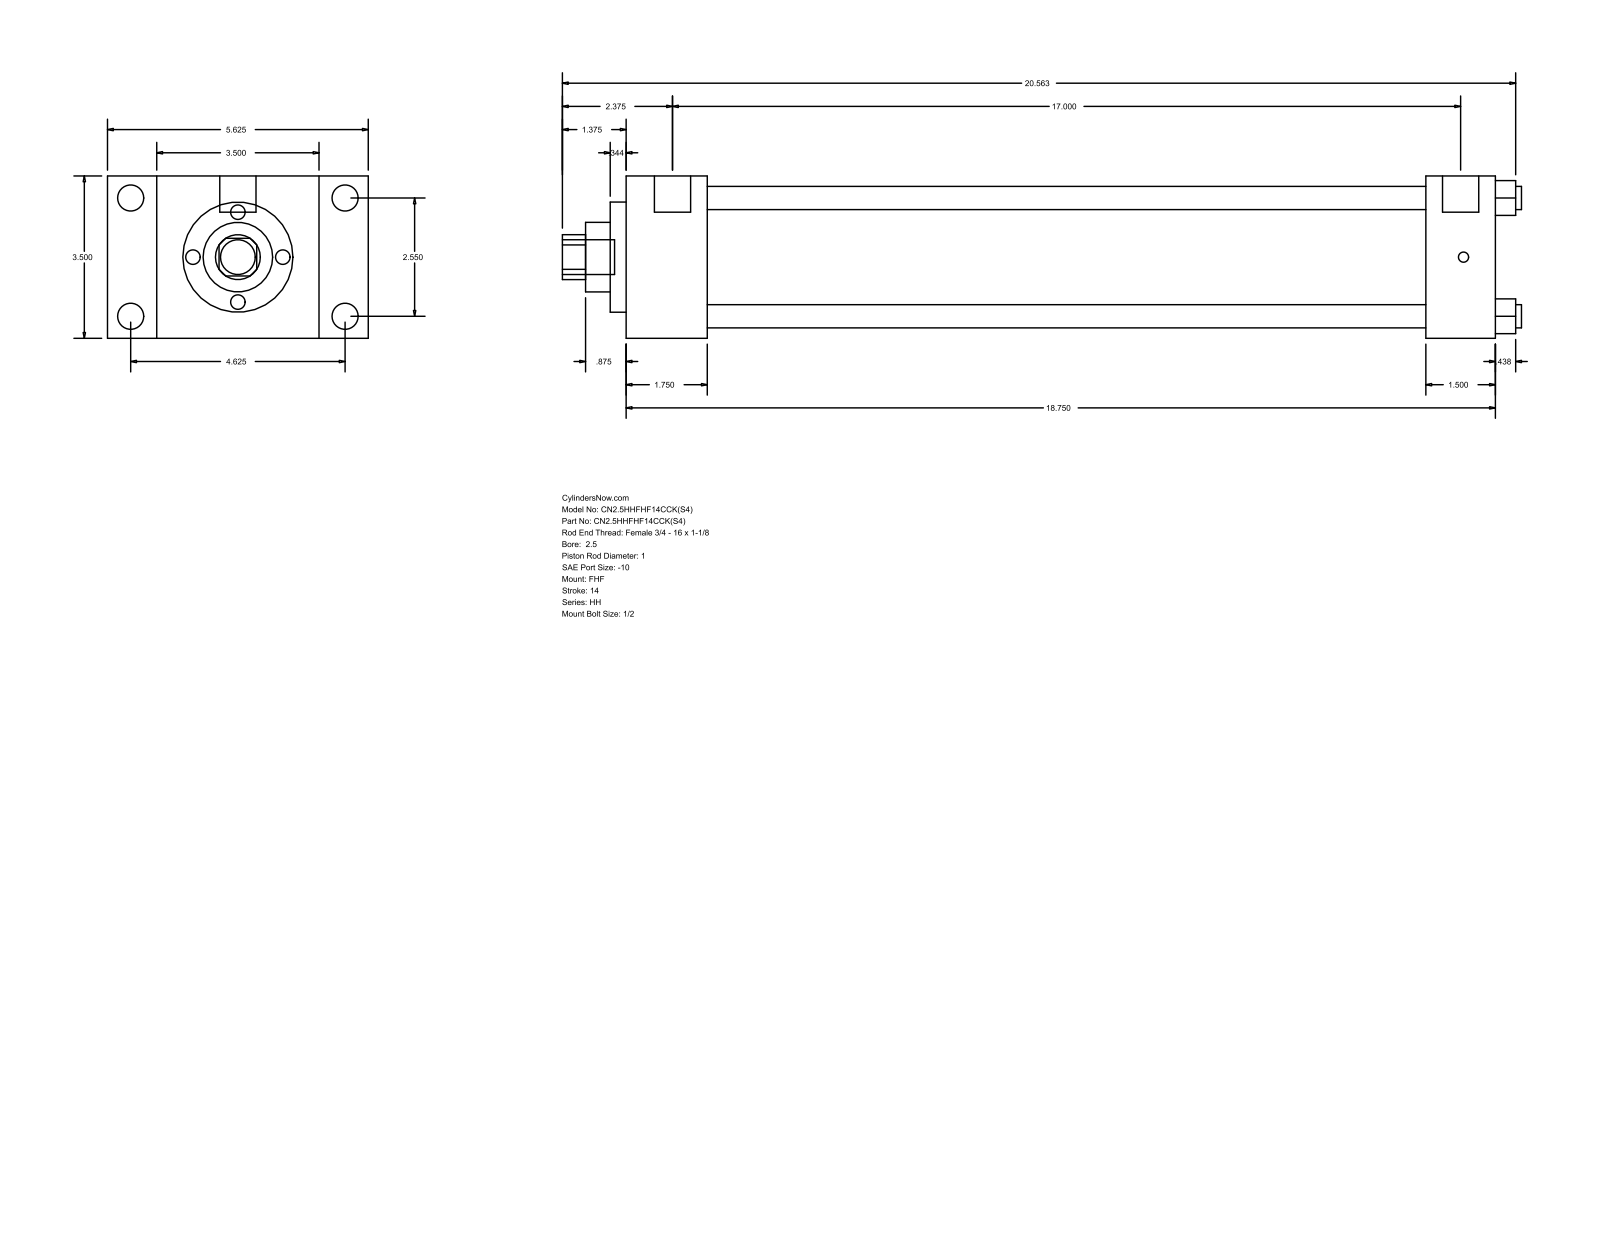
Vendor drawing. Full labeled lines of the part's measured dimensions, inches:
Part name (STEP PRODUCT): HH_FHF__0250_1
STEP written by: GSSL Pune (CONFIG_CONTROL_DESIGN)
Units: inches
Bodies: 0 solids, 90 faces (61 planar, 29 cylindrical, 0 other)
Overall size (bounding box): 20.687 × 5.625 × 3.5
Round holes (diameter × count): ⌀0.5 ×4, ⌀1 ×1, ⌀1.5 ×1, ⌀2.375 ×1, ⌀2.875 ×1
Round bosses / shafts (diameter × count): ⌀0.563 ×4, ⌀0.219 ×4, ⌀0.781 ×2, ⌀0.75 ×1
Partial cylindrical surfaces — rounded edges, fillets, slot ends (radius × count): R0.484 ×1
Main face-to-face distances: 3.5, 1.75, 1.063, 4.563, 18.75, 17, 5.625, 17.25, 15.5, 1.5
Hole centre spacings: 1.803, 2.55, 3.606
